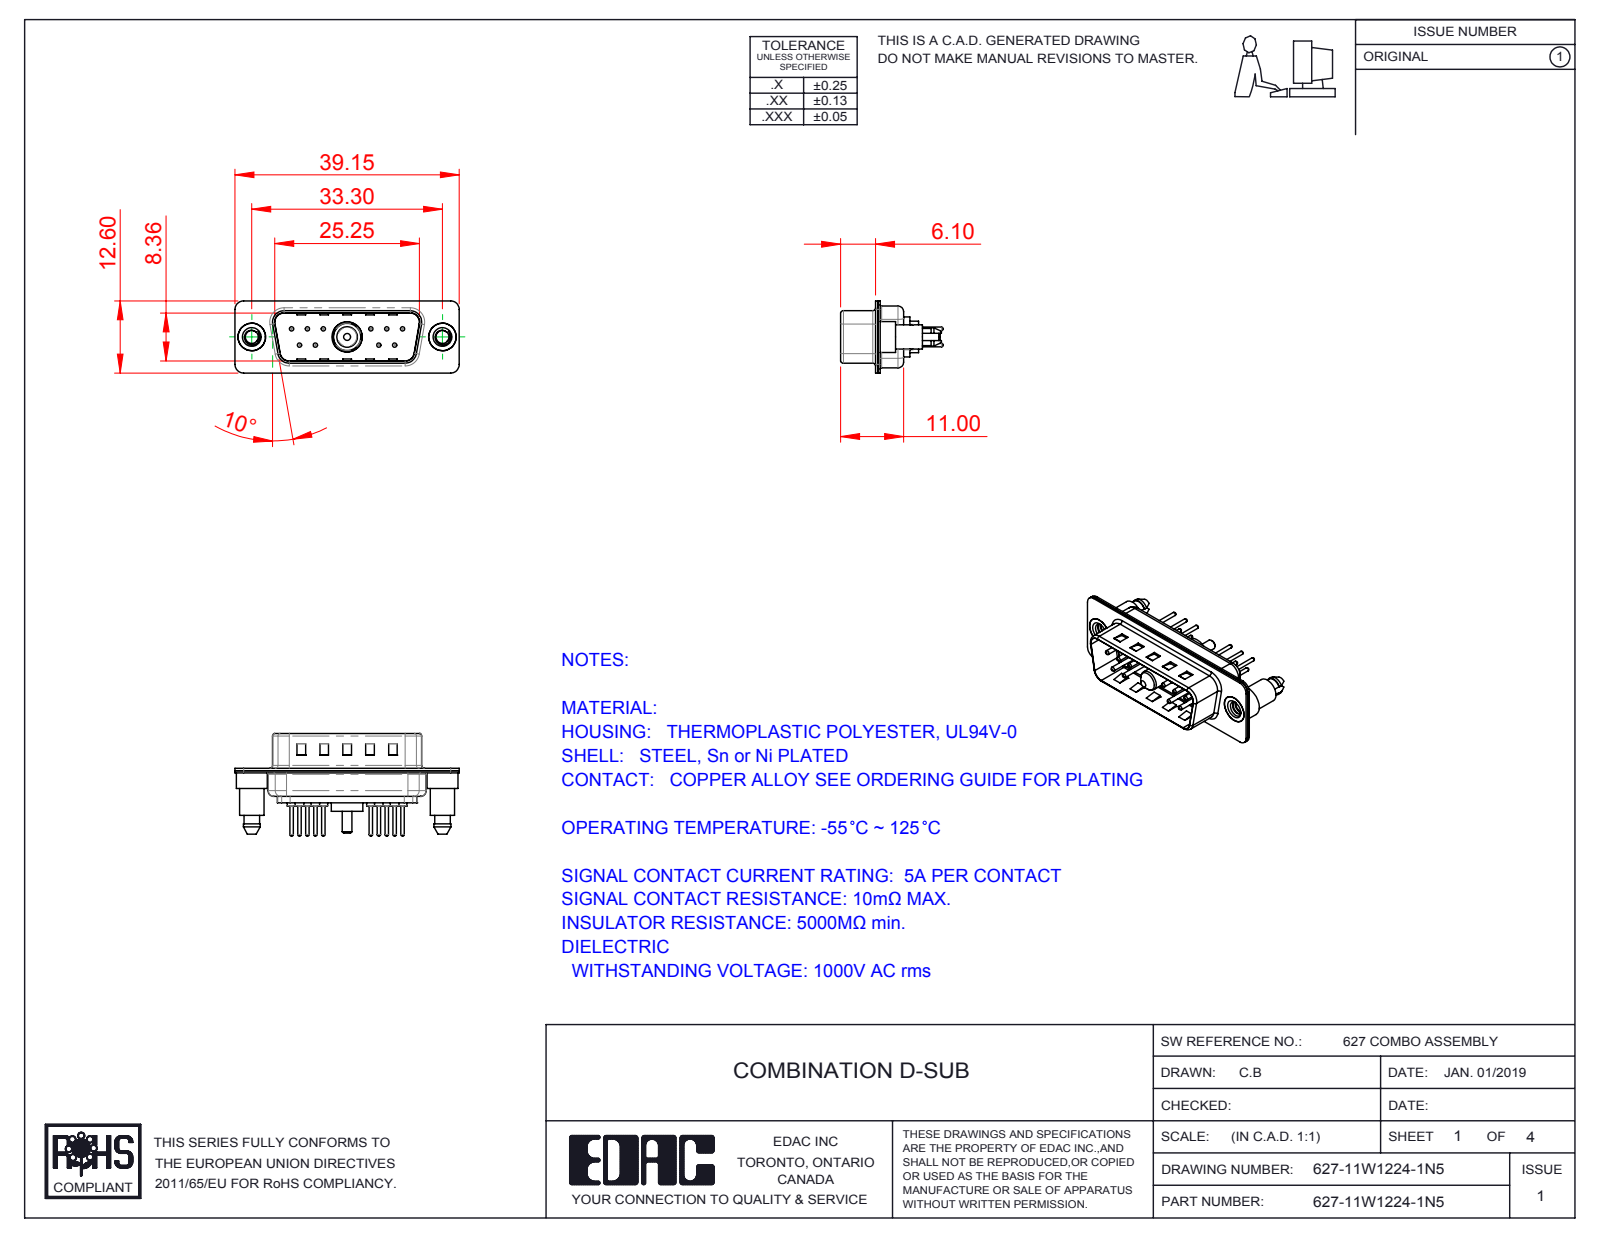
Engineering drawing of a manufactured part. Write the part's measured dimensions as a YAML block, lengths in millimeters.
part_name: "627-11W1224-1N5; 627Combo Shell Front_15 Contacts; 627Combo Threaded Boardlock_5; Power Pin_10A S (+4 more)"
step_written_by: "SolidWorks 2016 (CONFIG_CONTROL_DESIGN)"
units: millimeters
bodies: {solids: 17, faces: 813, planar: 244, cylindrical: 328, other: 241}
overall_size: [39.15, 17.9, 12.6]
volume: 2031
surface_area: 5110
round_holes:
  - {diameter: 0.75, count: 10}
  - {diameter: 1.6, count: 10}
  - {diameter: 2, count: 10}
  - {diameter: 2.26, count: 2}
  - {diameter: 4, count: 2}
  - {diameter: 4.8, count: 2}
  - {diameter: 4.85, count: 1}
  - {diameter: 5.3, count: 1}
round_bosses_or_shafts:
  - {diameter: 1.5, count: 10}
  - {diameter: 0.6, count: 10}
  - {diameter: 5.4, count: 2}
  - {diameter: 4.9, count: 2}
  - {diameter: 4.25, count: 2}
  - {diameter: 5.5, count: 1}
  - {diameter: 5.2, count: 1}
  - {diameter: 4.75, count: 1}
partial_cylinders:
  - {radius: 1.5, count: 22}
  - {radius: 2, count: 12}
  - {radius: 1.6, count: 10}
  - {radius: 0.5, count: 8}
  - {radius: 1, count: 7}
  - {radius: 0.25, count: 4}
  - {radius: 0.6, count: 4}
  - {radius: 0.65, count: 4}
face_to_face_distances: [0.4, 0.82, 9.58, 0.8, 8.76, 1.5, 5.2, 5.6, 1.4, 6]
hole_center_spacings: [3.16, 2.77, 13.85, 11.08, 16.62, 5.03, 5.04, 5.54]
